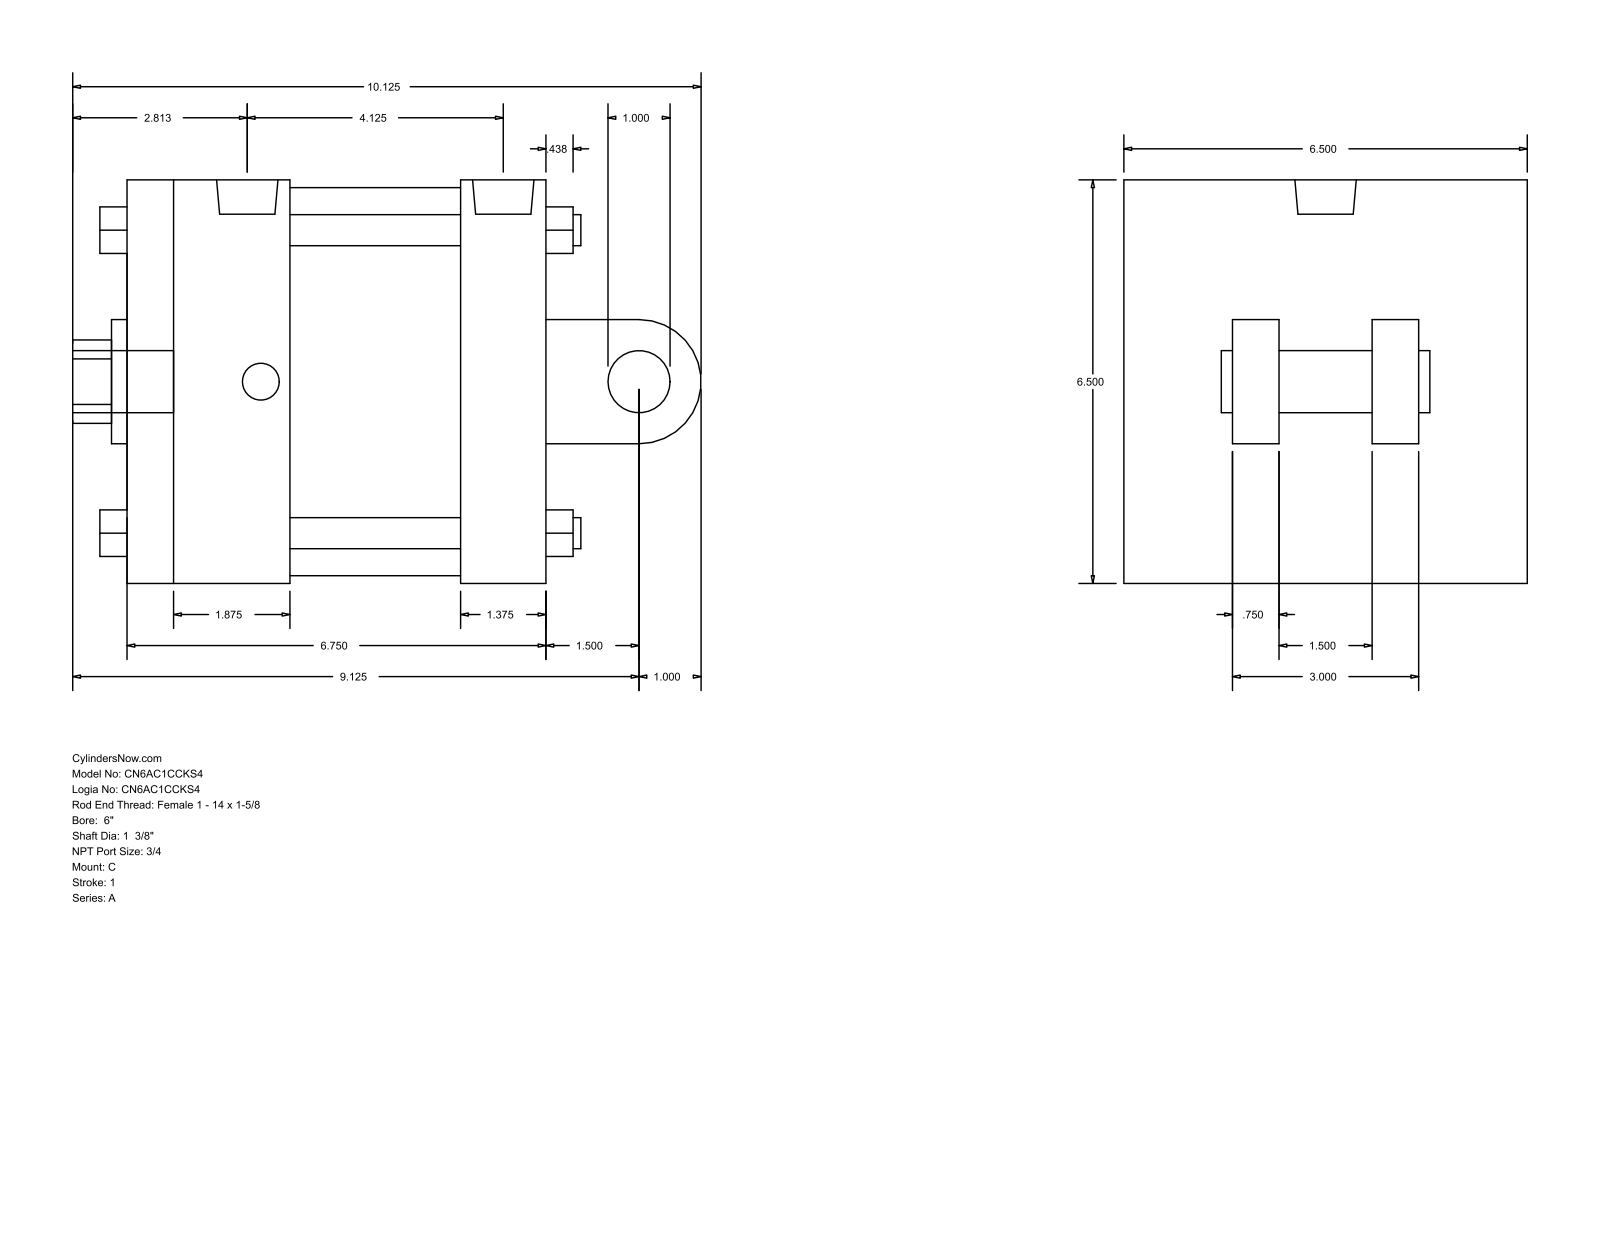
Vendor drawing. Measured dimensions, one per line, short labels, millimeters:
name: A_C__0600_1.375
written by: GSSL Pune (CONFIG_CONTROL_DESIGN)
unit: mm
bodies: 0 solids, 135 faces (102 planar, 33 cylindrical, 0 other)
size: 257.18 × 165.1 × 165.1
holes: 2× ⌀15.08, 1× ⌀25.12, 1× ⌀34.92, 1× ⌀50.8, 1× ⌀158.75
bosses: 4× ⌀12.7, 2× ⌀25.4, 2× ⌀15.08, 1× ⌀25.12
rounds: 1× R17.06, 1× R25.4
face distances: 165.1, 171.45, 19.05, 57.15, 66.67, 104.78, 136.52, 69.85, 34.93, 44.45
hole spacings: 5.56
